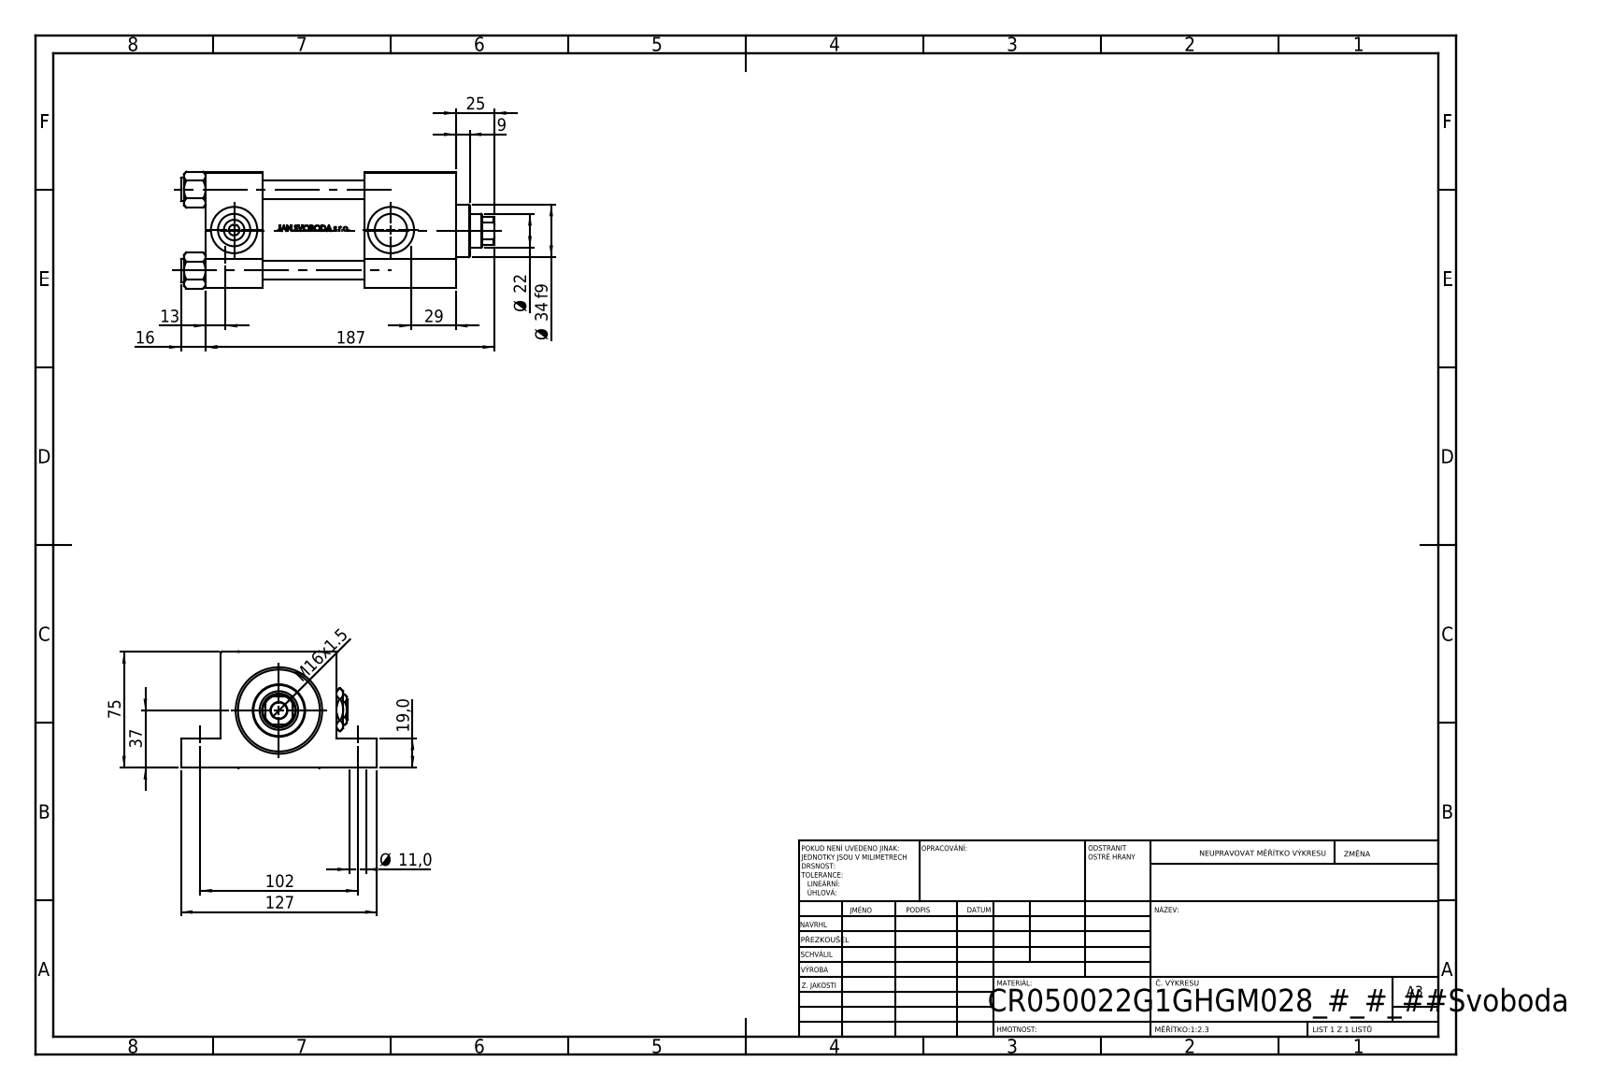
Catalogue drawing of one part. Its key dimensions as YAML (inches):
part_name: "V215CR_VCP_G; V215CR_G_TYCINKA; Zatka_pro_OIL_PORT; V215CR_G_Body (+2 more)"
step_written_by: "SolidWorks 2019 (CONFIG_CONTROL_DESIGN)"
units: inches
bodies: {solids: 12, faces: 1134, planar: 454, cylindrical: 128, other: 552}
overall_size: [7.992, 5, 2.974]
volume: 46.56
surface_area: 256.9
round_holes:
  - {diameter: 0.433, count: 4}
  - {diameter: 0.472, count: 4}
  - {diameter: 0.276, count: 2}
  - {diameter: 0.825, count: 2}
  - {diameter: 1.181, count: 2}
  - {diameter: 0.413, count: 1}
  - {diameter: 0.866, count: 1}
  - {diameter: 0.984, count: 1}
  - {diameter: 1.614, count: 1}
  - {diameter: 1.969, count: 1}
  - {diameter: 2.087, count: 1}
round_bosses_or_shafts:
  - {diameter: 0.591, count: 4}
  - {diameter: 2.205, count: 1}
  - {diameter: 1.339, count: 1}
partial_cylinders:
  - {radius: 0.413, count: 1}
face_to_face_distances: [2.953, 1.457, 6.378, 4.921, 0.748, 2.205, 4.055, 2.598, 2.323, 1.024]
hole_center_spacings: [2.059, 1.442, 1.47, 2.912, 4.016, 4.724, 6.2, 3.996]
